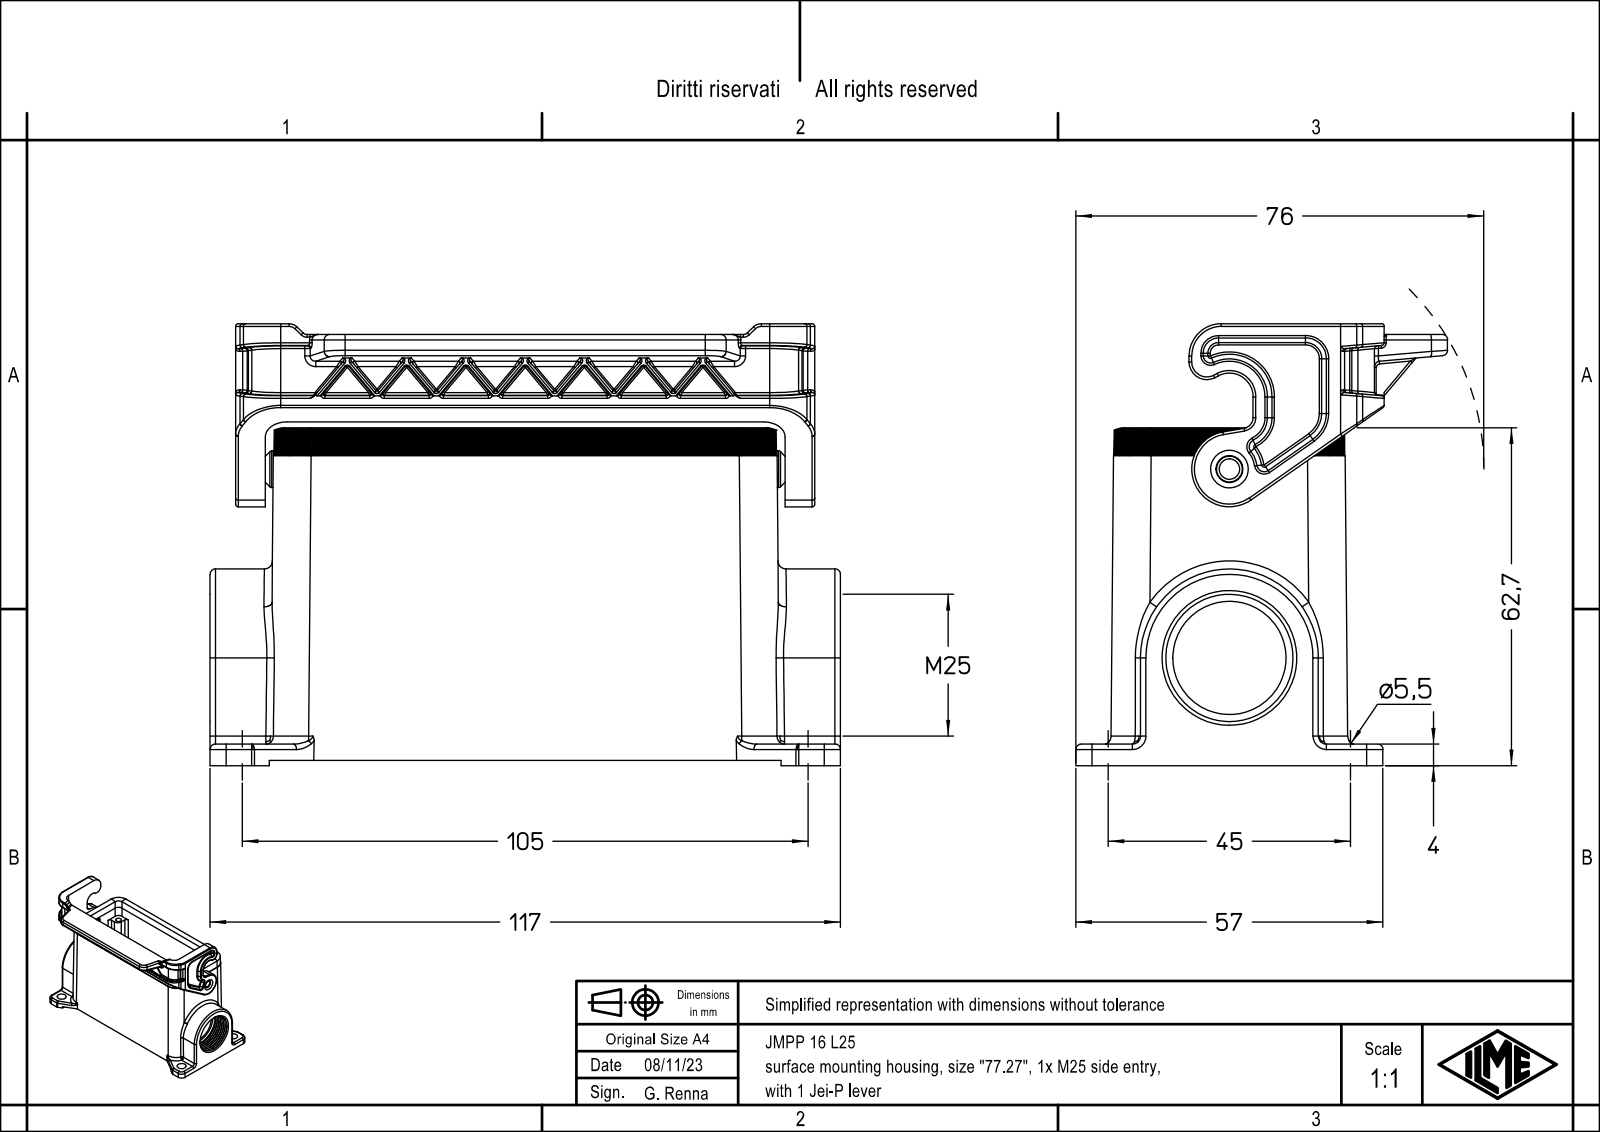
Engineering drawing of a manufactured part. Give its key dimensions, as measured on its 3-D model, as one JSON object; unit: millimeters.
{"part_name": "JMPP 16 L25", "step_written_by": "Creo Elements/Direct Modeling 20.1B 02-Apr-2019 (C) Parametric Technology GmbH (AUTOMOTIVE_DESIGN)", "units": "millimeters", "bodies": {"solids": 1, "faces": 875, "planar": 183, "cylindrical": 354, "other": 338}, "overall_size": [117, 82, 69], "volume_mm3": 119505, "surface_area_mm2": 55101, "round_holes": [[3, 4], [3.5, 4], [5.5, 4], [4.8, 1], [21, 1], [23.6, 1]], "round_bosses_or_shafts": [[6.8, 1]], "partial_cylinders_radius": [[0.3, 99], [0.5, 77], [1, 27], [3, 16], [1.5, 12], [2, 9], [7, 9], [4, 8]], "face_to_face_distances": [3, 1, 4, 10.25, 106.75, 80, 79, 76, 2, 7], "hole_center_spacings": [16.43, 38.54, 91.69, 98.09, 27, 45, 77.5, 82.07]}
